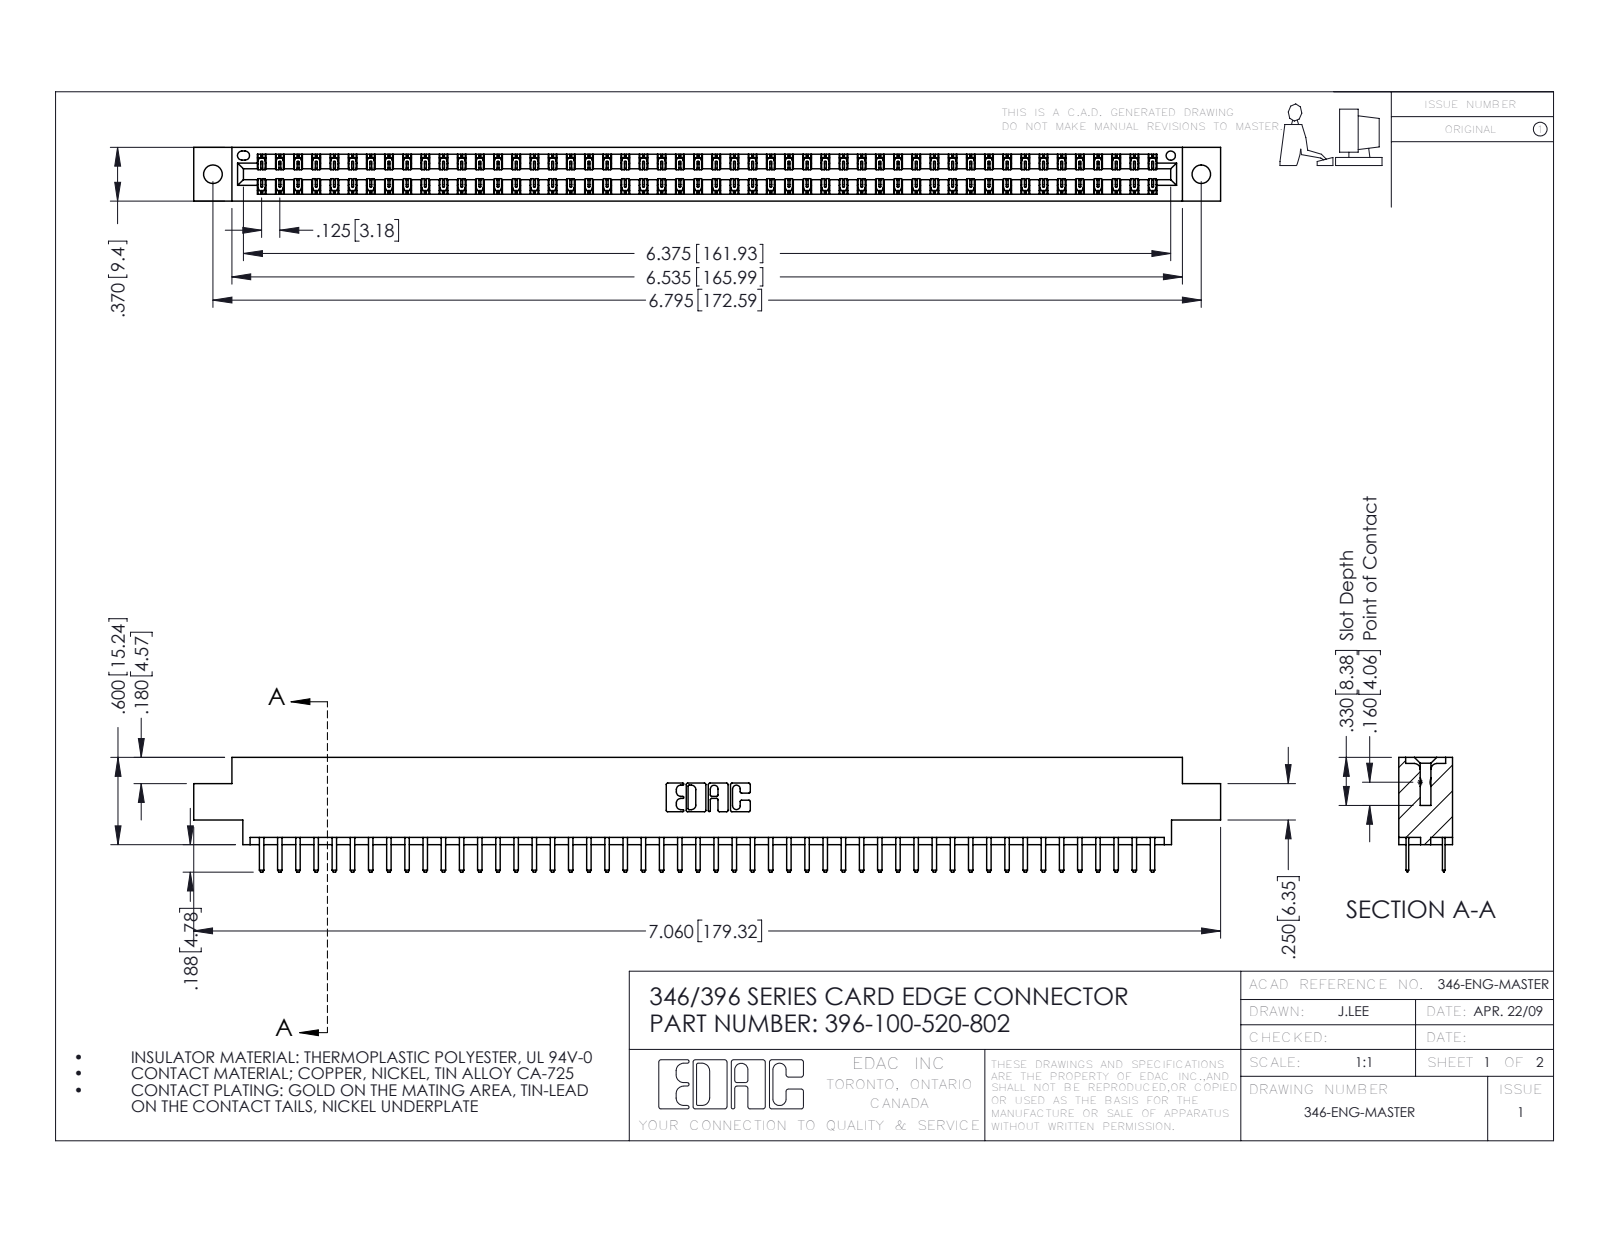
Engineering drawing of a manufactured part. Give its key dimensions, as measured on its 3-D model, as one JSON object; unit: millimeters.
{"part_name": "396-100-520-802; 346 Part_0.170 Offset - 0.128 Dia; 345-292-001_345-293-120", "step_written_by": "SolidWorks 2016 (CONFIG_CONTROL_DESIGN)", "units": "millimeters", "bodies": {"solids": 101, "faces": 5726, "planar": 3780, "cylindrical": 1946, "other": 0}, "overall_size": [179.3, 20, 9.4], "volume_mm3": 17320, "surface_area_mm2": 23730, "round_holes": [[3.3, 2], [1.6, 1]], "partial_cylinders_radius": [[0.2, 150], [0.3, 104], [0.3, 22], [0.2, 6], [0.8, 6], [0.7, 3], [0.4, 2], [0.6, 2]], "face_to_face_distances": [1.2, 8.2, 6.4, 9.4, 7, 1.8, 7.6, 0.6, 3.8, 5.6], "hole_center_spacings": [6.2, 167.3, 172.6]}
